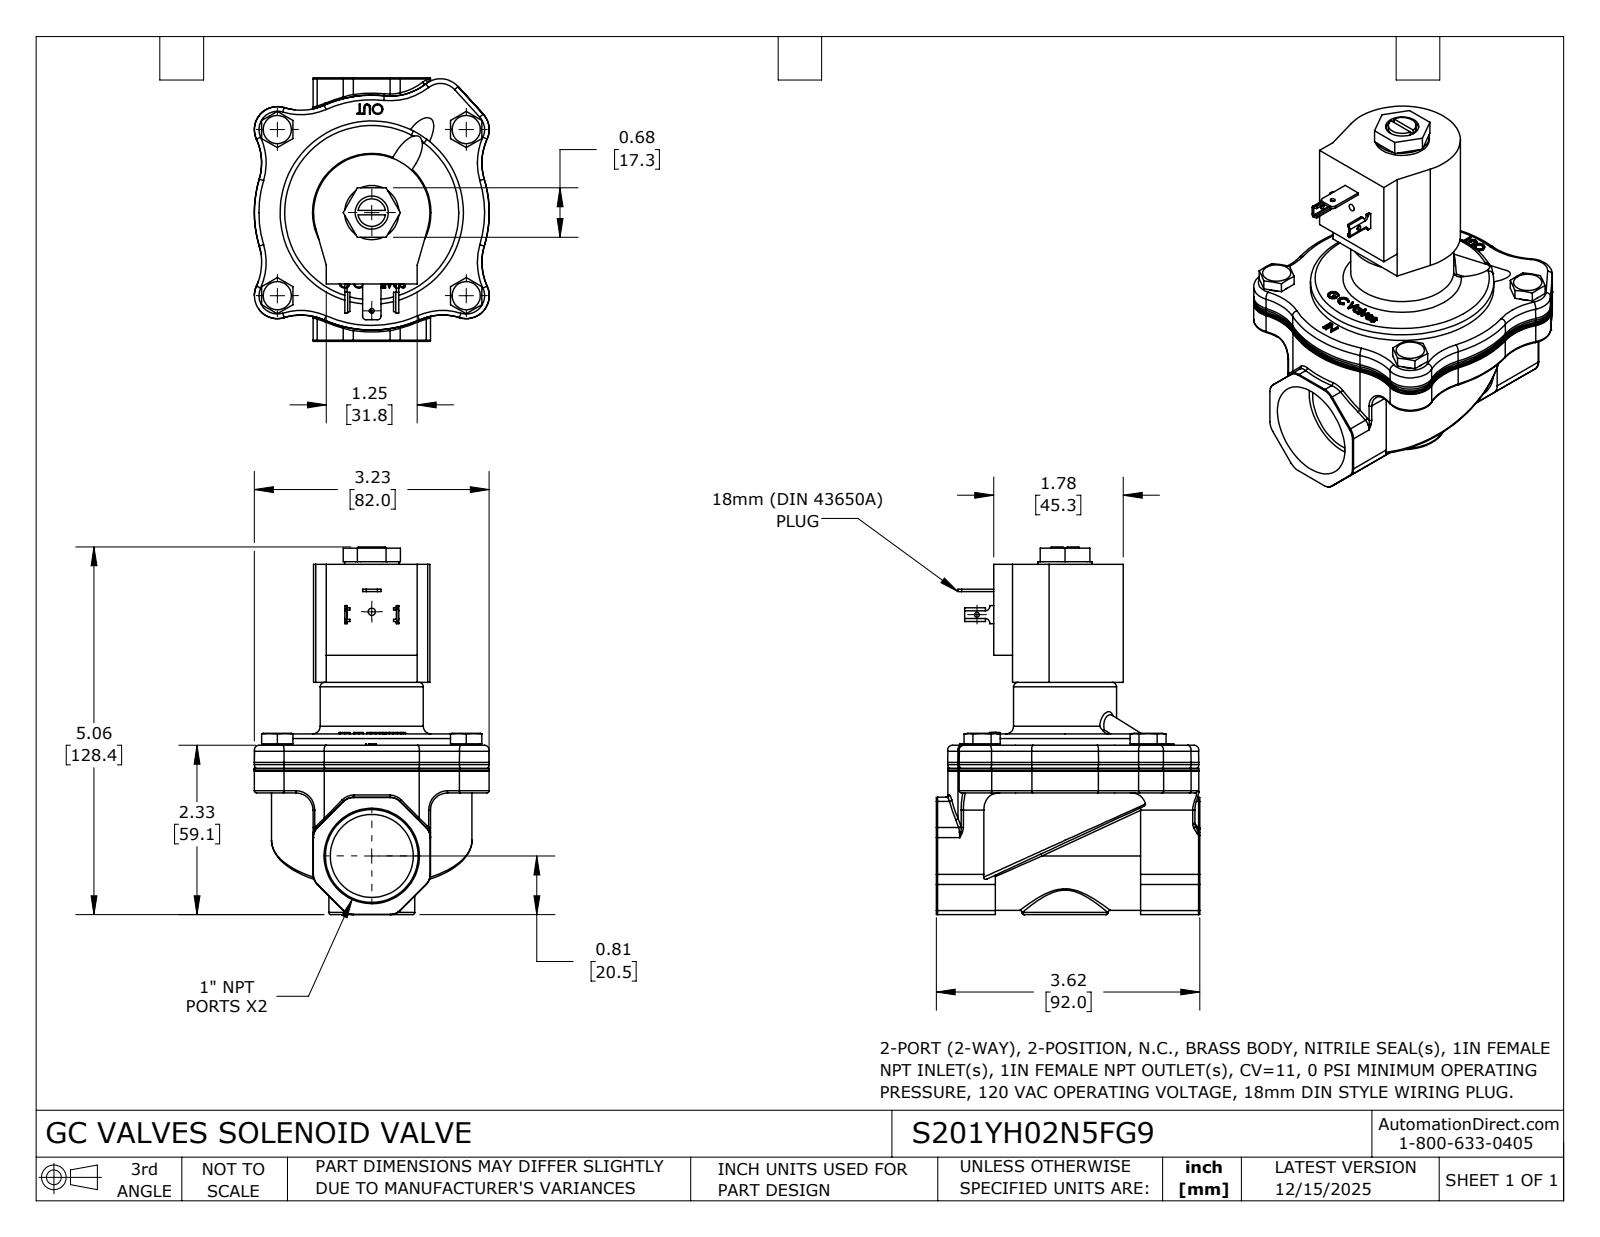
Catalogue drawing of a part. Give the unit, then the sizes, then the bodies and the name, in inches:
Units: inches
Overall size (bounding box): 5.055 × 3.622 × 3.232
Round holes (diameter × count): ⌀0.066 ×1, ⌀0.067 ×1, ⌀0.1 ×1, ⌀0.456 ×1, ⌀1.141 ×1
Round bosses / shafts (diameter × count): ⌀0.388 ×4, ⌀2.52 ×1, ⌀1.417 ×1, ⌀1.181 ×1, ⌀0.746 ×1, ⌀0.38 ×1
Partial cylindrical surfaces — rounded edges, fillets, slot ends (radius × count): R0.031 ×24, R0.787 ×24, R0.315 ×12, R0.197 ×8, R0.006 ×4, R0.041 ×4, R0.05 ×2, R0.06 ×2
Main face-to-face distances: 0.157, 0.655, 0.812, 3.141, 2.486, 2.329, 2.485, 2.328, 1.673, 4.814
Hole centre spacings: 1.35, 3.356
Volume: 19.13 in³ · Surface area: 70.49 in²
Bodies: 1 solid, 671 faces (220 planar, 172 cylindrical, 279 other)
Part name (STEP PRODUCT): S201YH02N5FG9
STEP written by: SolidWorks 2024 (CONFIG_CONTROL_DESIGN)
